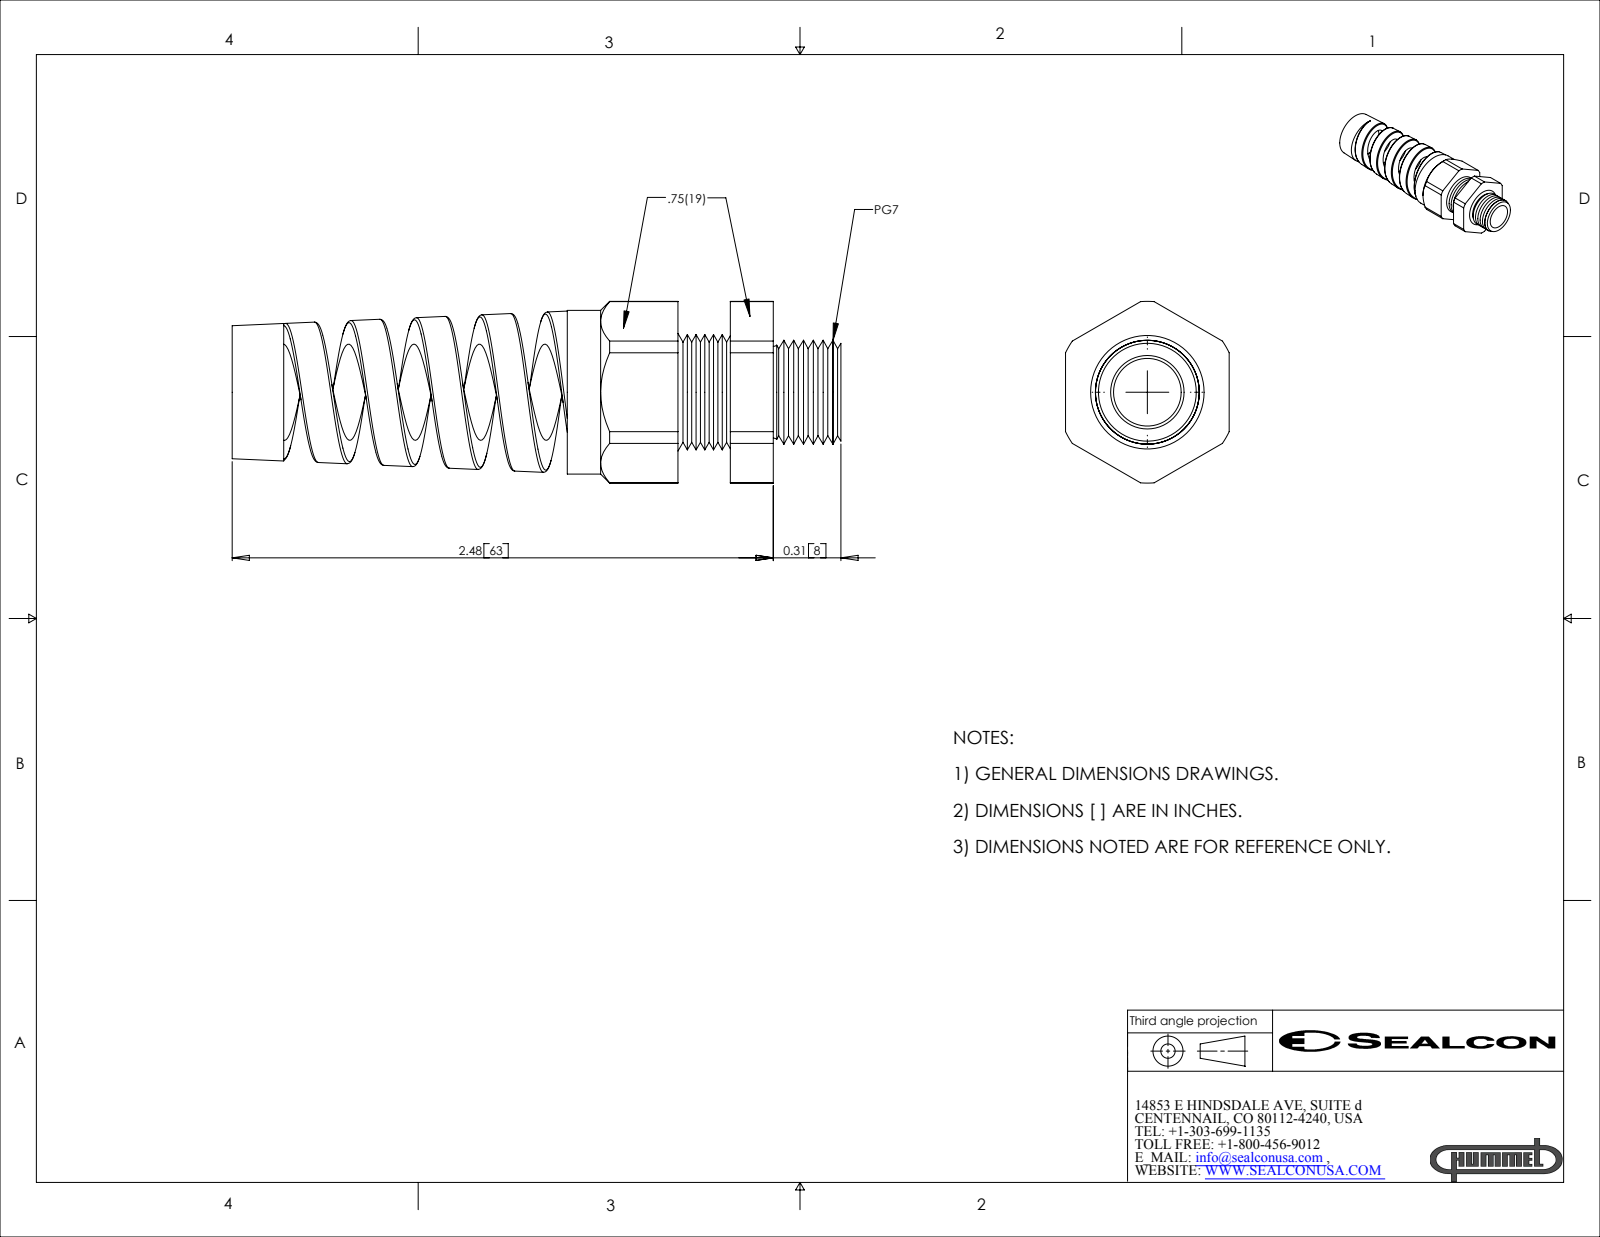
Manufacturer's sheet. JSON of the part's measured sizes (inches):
{"part_name": "CF07GA-GY", "step_written_by": "SolidWorks 2007 (CONFIG_CONTROL_DESIGN)", "units": "inches", "bodies": {"solids": 2, "faces": 144, "planar": 24, "cylindrical": 35, "other": 85}, "overall_size": [2.79, 0.833, 0.75], "volume_in3": 0.497, "surface_area_in2": 12.31, "round_holes": [[0.31, 1], [0.441, 1], [0.539, 1]], "round_bosses_or_shafts": [[0.75, 1]], "partial_cylinders_radius": [[0.231, 1], [0.416, 1]], "face_to_face_distances": [0.75, 0.437, 0.24, 0.197, 0.75, 0.507, 0.748, 0.944, 1.536, 2.043]}
